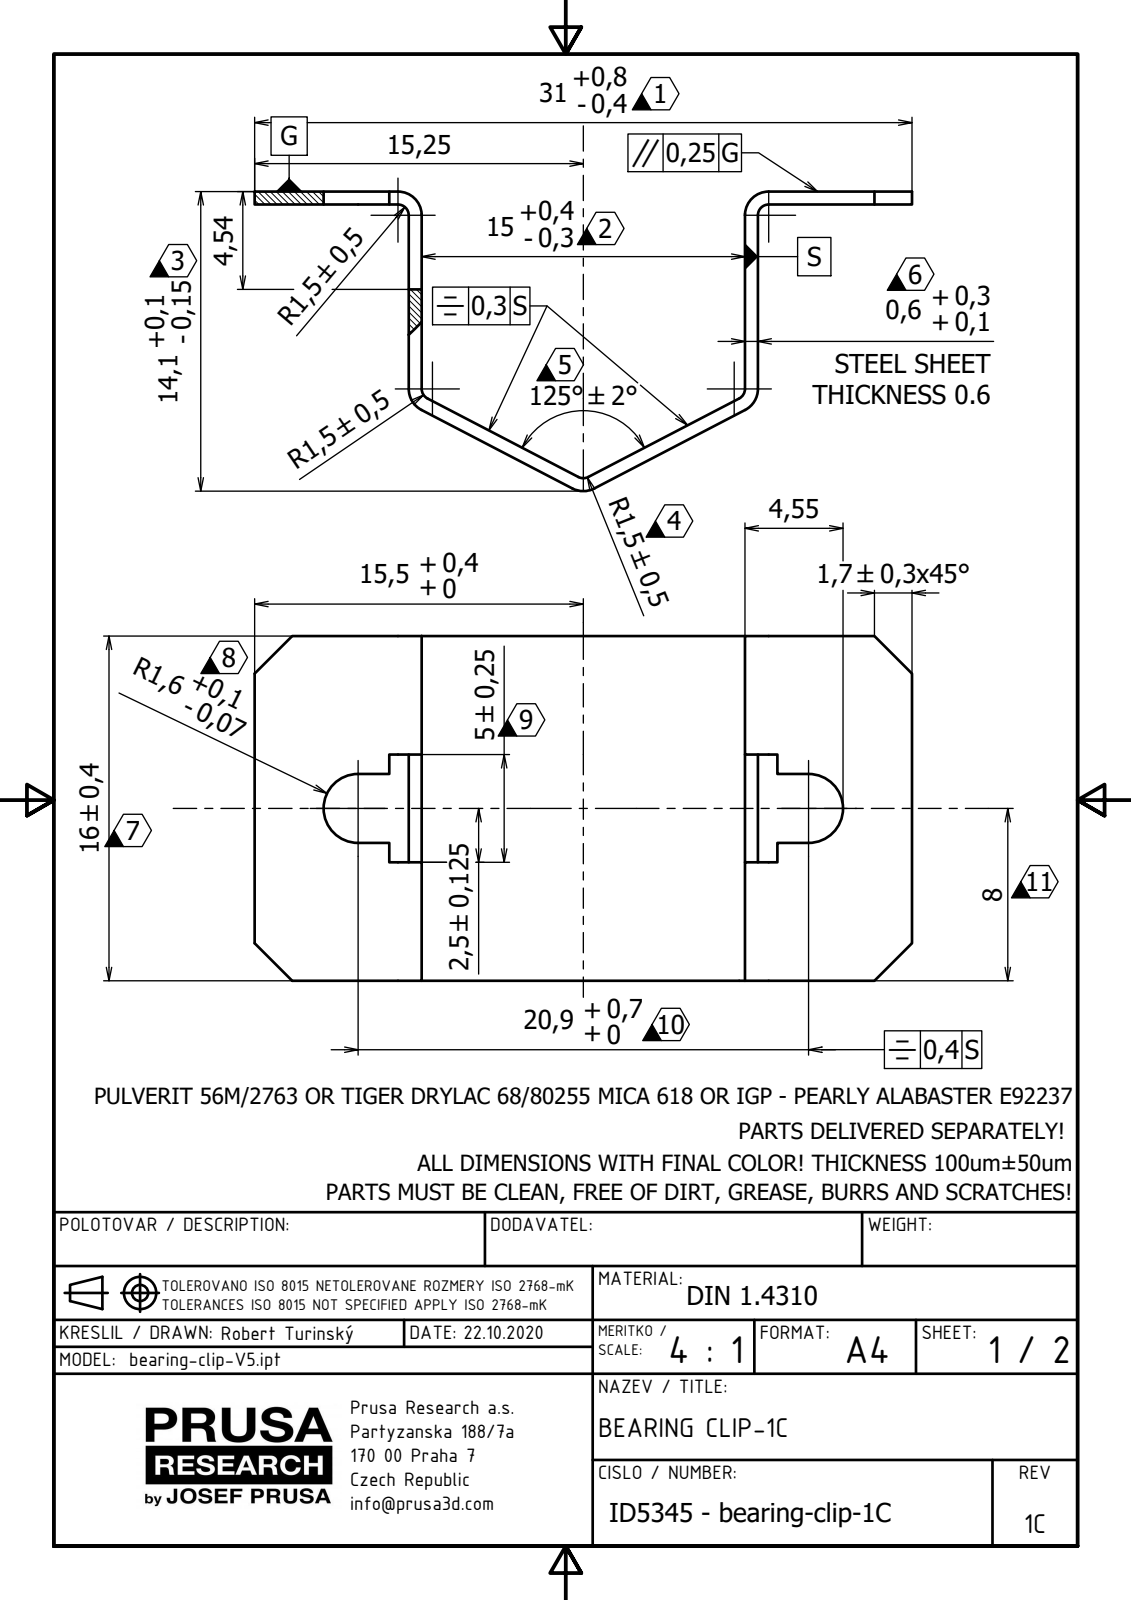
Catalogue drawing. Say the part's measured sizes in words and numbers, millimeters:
The part is named "bearing-clip-V5". Its 3-D file was written by "Autodesk Inventor 2021 (AUTOMOTIVE_DESIGN)". It is 1 solid with 70 faces: 54 planar, 16 cylindrical and 0 other. Overall it measures 30.5 by 16 by 13.9 millimeters. Its volume is 438 cubic millimeters and its surface area 1 566 square millimeters. Partial cylindrical surfaces (rounded edges, fillets, slot ends): 5 of radius 0.5, 5 of radius 1.1, 2 of radius 1.6. The main face-to-face distances are 0.6, 15.6, 16.2, 15, 16, 7.15, 7.75, 22.75, 23.35, 5.5.
